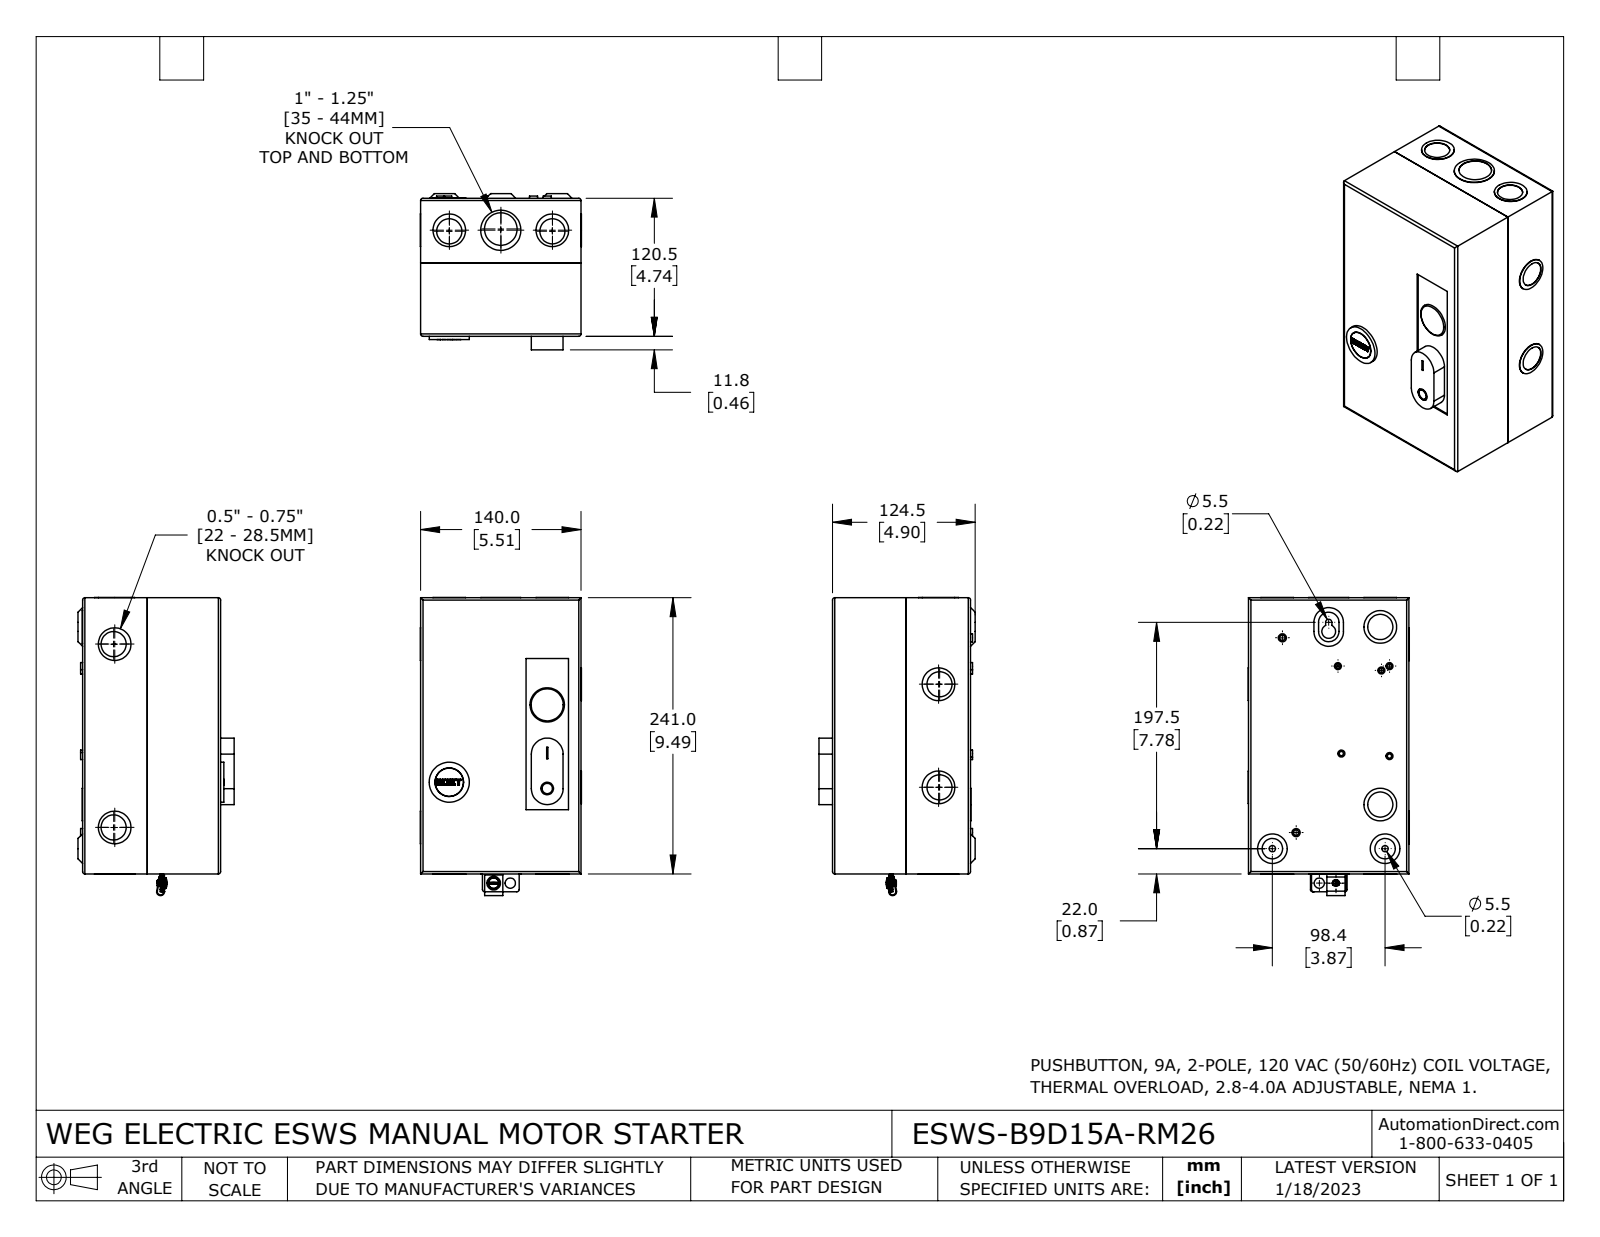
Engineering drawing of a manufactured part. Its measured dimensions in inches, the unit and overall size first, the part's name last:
Units: inches
Overall size (bounding box): 10.248 × 5.535 × 5.366
Round holes (diameter × count): ⌀0.146 ×5, ⌀0.864 ×4, ⌀0.183 ×2, ⌀0.217 ×2, ⌀0.354 ×2, ⌀0.864 ×2, ⌀0.866 ×2, ⌀0.886 ×2, ⌀0.256 ×1, ⌀0.303 ×1, ⌀0.433 ×1, ⌀0.469 ×1
Round bosses / shafts (diameter × count): ⌀1.124 ×6, ⌀0.24 ×5, ⌀1.122 ×2, ⌀0.278 ×2, ⌀1.38 ×1, ⌀1.378 ×1, ⌀1.193 ×1, ⌀1.148 ×1
Partial cylindrical surfaces — rounded edges, fillets, slot ends (radius × count): R0.004 ×34, R0.079 ×13, R0.031 ×4, R0.108 ×3, R0.059 ×2, R0.075 ×2, R0.122 ×2, R0.138 ×2
Main face-to-face distances: 0.047, 4.697, 5.465, 4.65, 9.441, 4.744, 5.417, 5.512, 0.071, 0.063
Hole centre spacings: 0.571, 1.378, 1.773, 3.387, 3.543, 4.921, 5.995, 7.484
Volume: 16.23 in³ · Surface area: 585.2 in²
Bodies: 7 solids, 435 faces (168 planar, 230 cylindrical, 37 other)
Part name (STEP PRODUCT): ESWS-B9D15A-RM26
STEP written by: SolidWorks 2021 (CONFIG_CONTROL_DESIGN)
